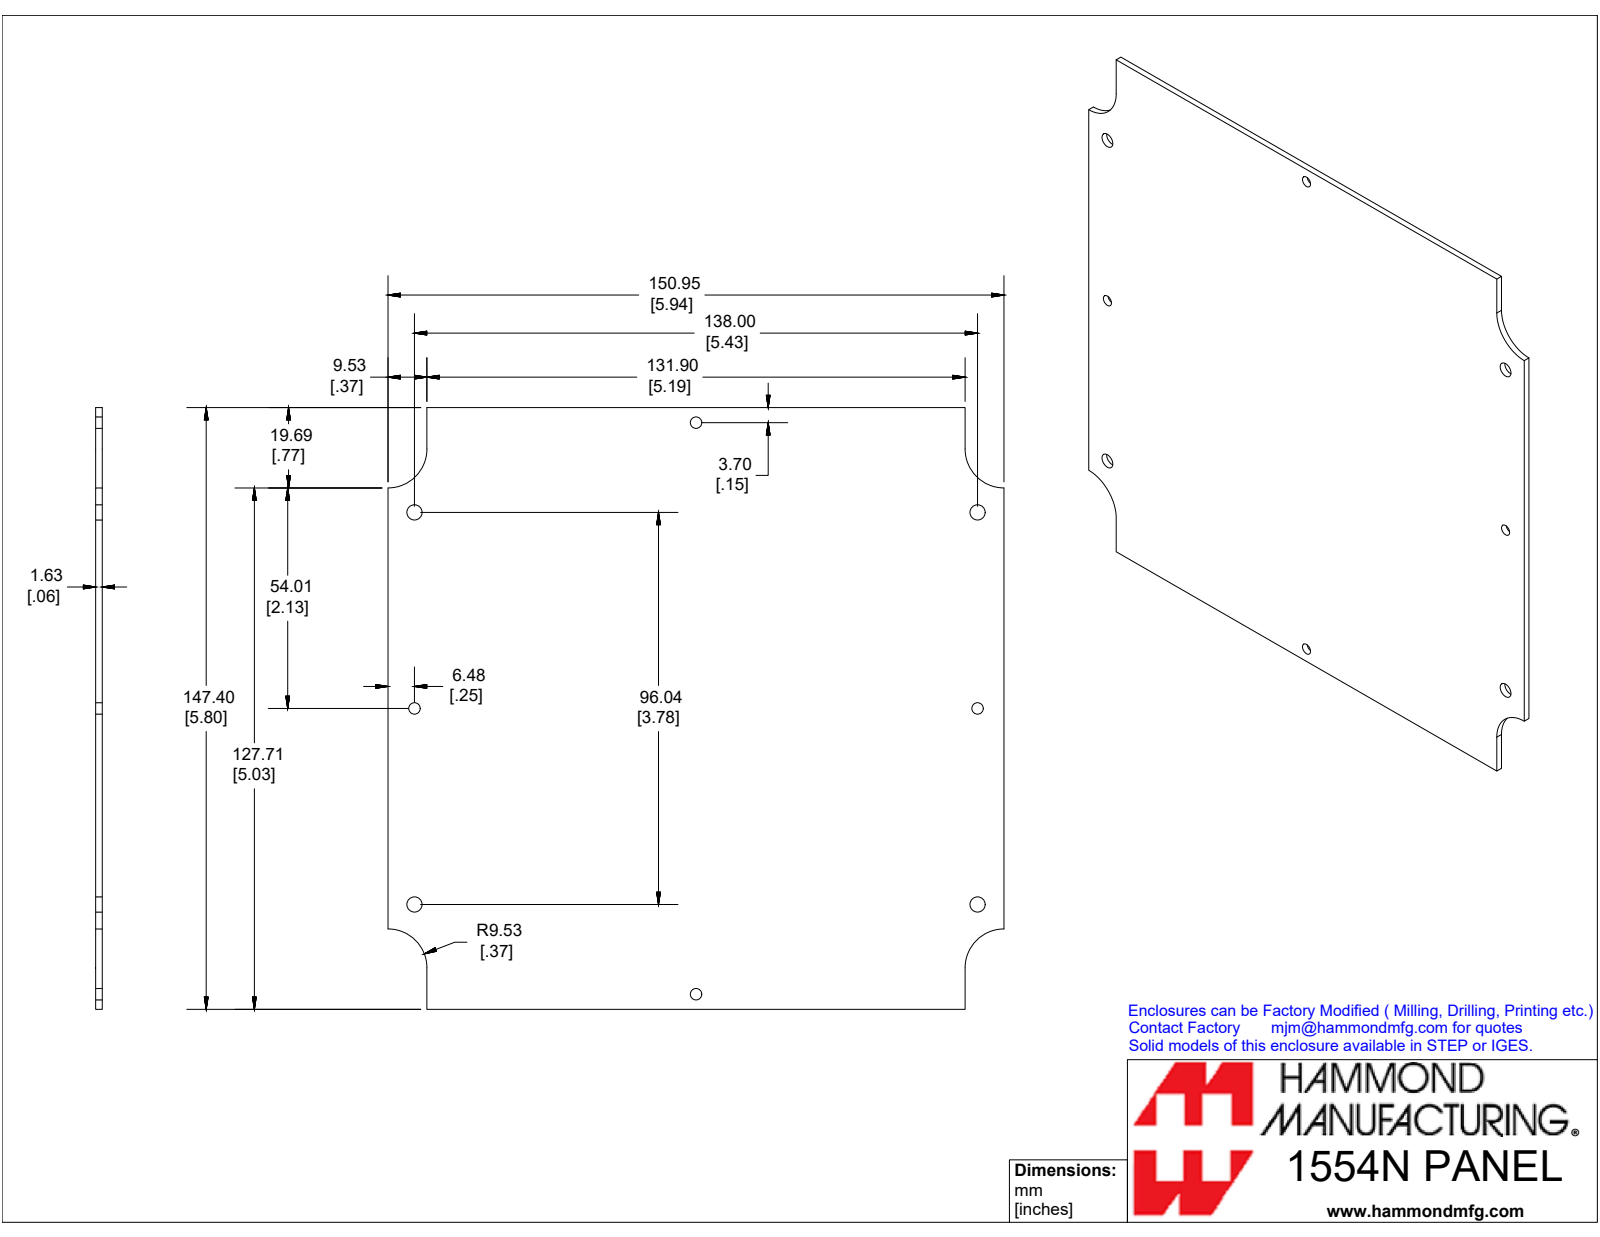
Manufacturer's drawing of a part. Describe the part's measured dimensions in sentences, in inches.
The part is named "1554RPL". Its 3-D file was written by "SolidWorks 2019 (CONFIG_CONTROL_DESIGN)". It is 1 solid with 22 faces: 10 planar, 12 cylindrical and 0 other. Overall it measures 5.943 by 5.803 by 0.064 inches. Its volume is 2.134 cubic inches and its surface area 68.35 square inches. Round holes: 4 of diameter 0.11, 4 of diameter 0.147. Partial cylindrical surfaces (rounded edges, fillets, slot ends): 4 of radius 0.375. The main face-to-face distances are 0.064, 5.803, 5.943, 0.375, 5.568, 5.193. The hole center spacings are 1.891, 2.851, 3.87, 5.382, 5.753, 5.433, 3.781, 6.619.
